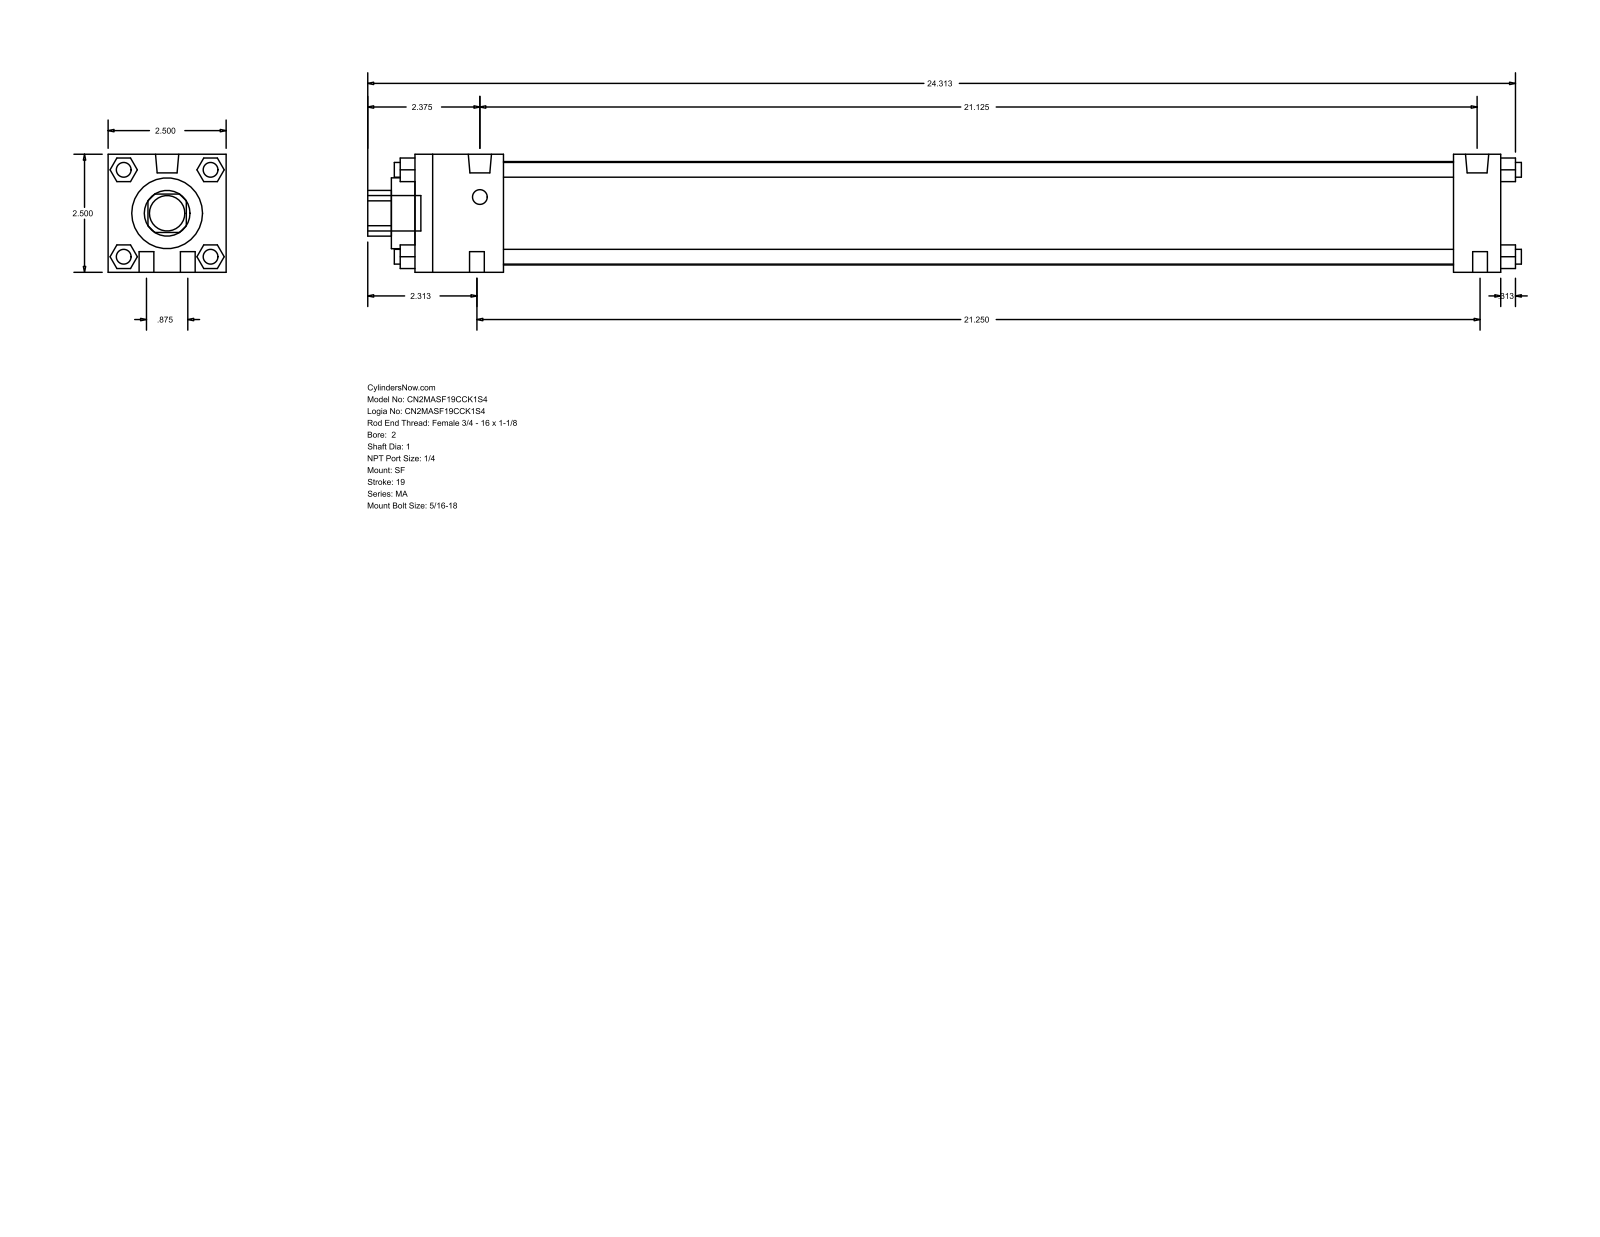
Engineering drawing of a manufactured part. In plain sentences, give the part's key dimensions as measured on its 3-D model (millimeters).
The part is named "MA_SF__0200_1". Its 3-D file was written by "GSSL Pune (CONFIG_CONTROL_DESIGN)". It is 0 solids with 124 faces: 94 planar, 30 cylindrical and 0 other. Overall it measures 620.71 by 63.5 by 63.5 millimeters. Round holes: 1 of diameter 25.4, 1 of diameter 38.1, 1 of diameter 55.63. Round bosses or shafts: 10 of diameter 7.94, 2 of diameter 12.49, 1 of diameter 19.05. Partial cylindrical surfaces (rounded edges, fillets, slot ends): 1 of radius 12.29. The main face-to-face distances are 63.5, 584.2, 12.7, 25.4, 558.8, 47.63, 511.17, 536.57, 40.47, 23.37.
